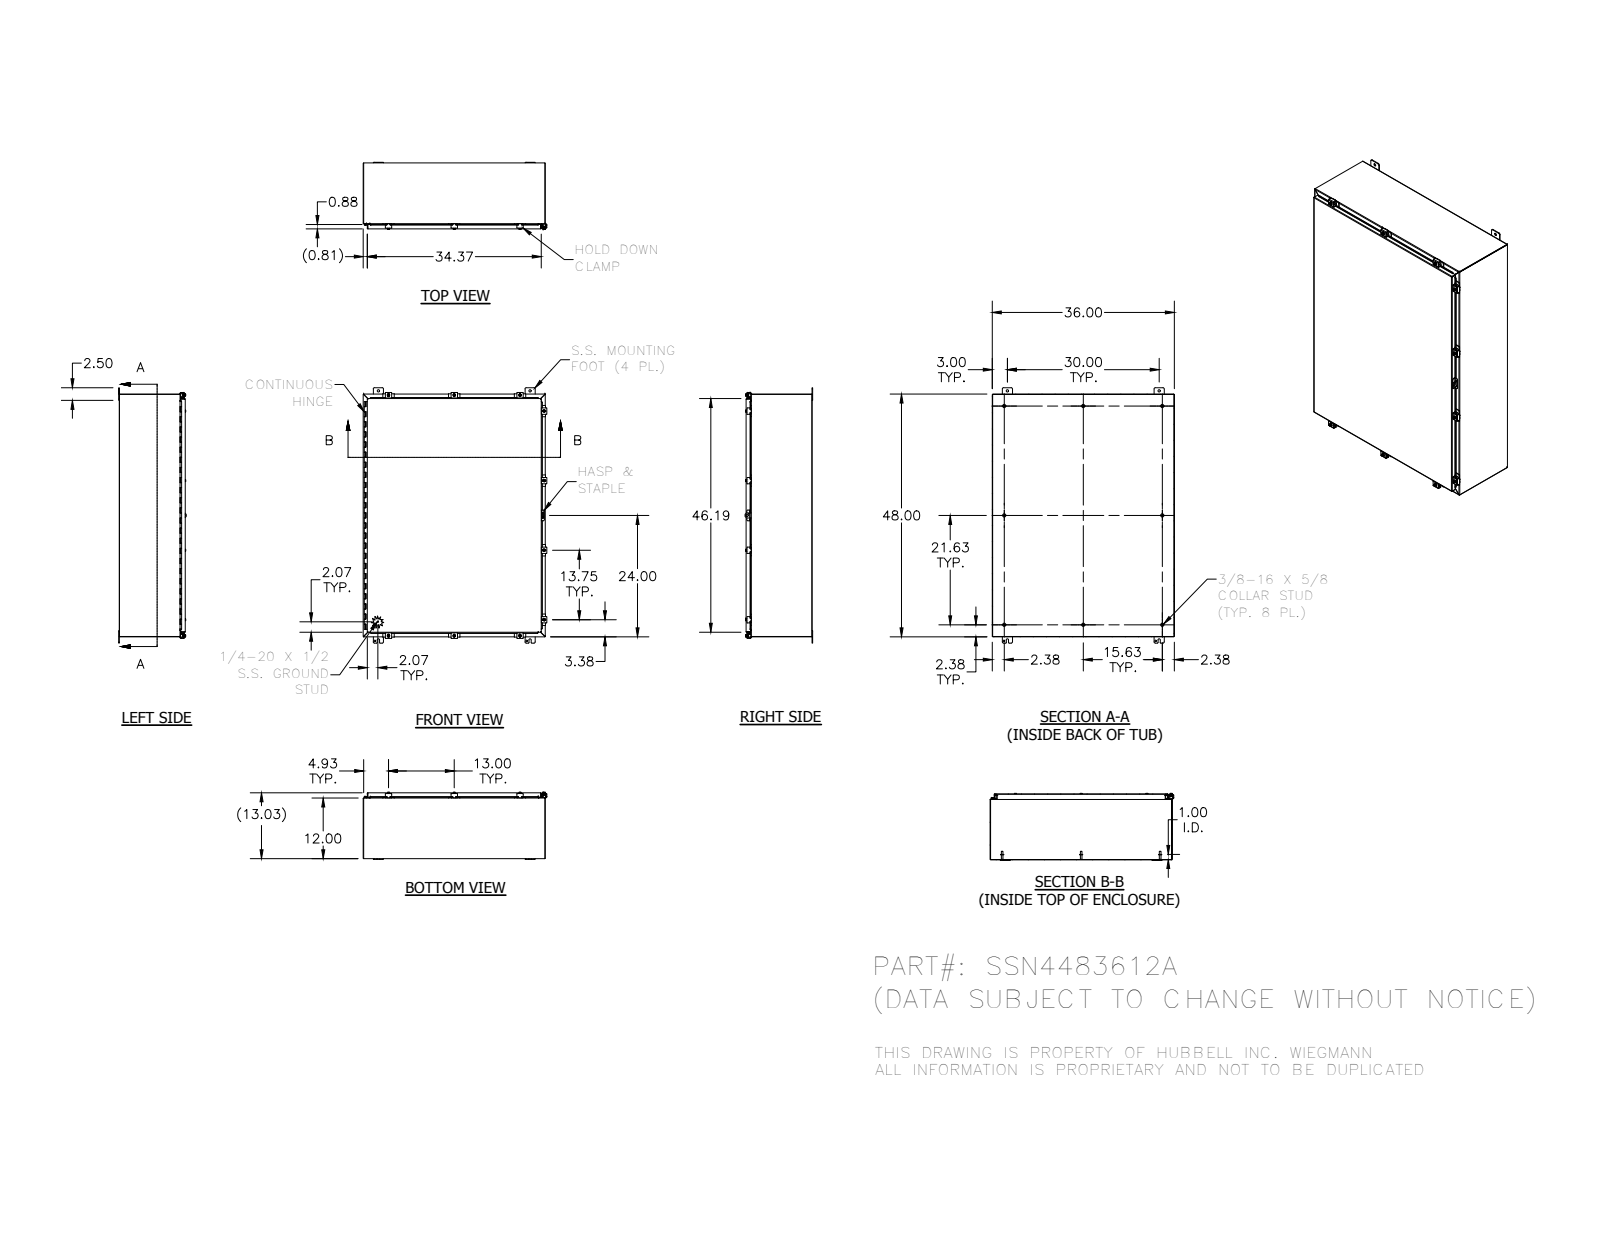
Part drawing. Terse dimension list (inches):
name: HFW308001; 38415; SSN4483612ALRS; 32874-48L (+8 more)
written by: SolidWorks 2014 (AUTOMOTIVE_DESIGN)
unit: in
bodies: 73 solids, 2680 faces (1093 planar, 1174 cylindrical, 413 other)
size: 50.5 × 36.311 × 13.355
volume: 463 in³; area: 12 292 in²
holes: 10× ⌀0.211, 10× ⌀0.281, 10× ⌀0.3, 4× ⌀0.313, 4× ⌀0.438, 1× ⌀0.125, 1× ⌀0.156, 1× ⌀0.5
bosses: 12× ⌀0.25, 10× ⌀0.52, 10× ⌀0.5, 10× ⌀0.35, 8× ⌀0.625, 8× ⌀0.33, 1× ⌀0.337, 1× ⌀0.12
rounds: 117× R0.03, 41× R0.125, 37× R0.25, 21× R0.031, 21× R0.105, 20× R0.141, 18× R0.062, 14× R0.1
face distances: 0.074, 12.959, 12.885, 13.033, 35.926, 47.926, 35.852, 36, 47.852, 48
hole spacings: 13.75, 1.593, 13, 18.091, 27.5, 30, 30.973, 48
